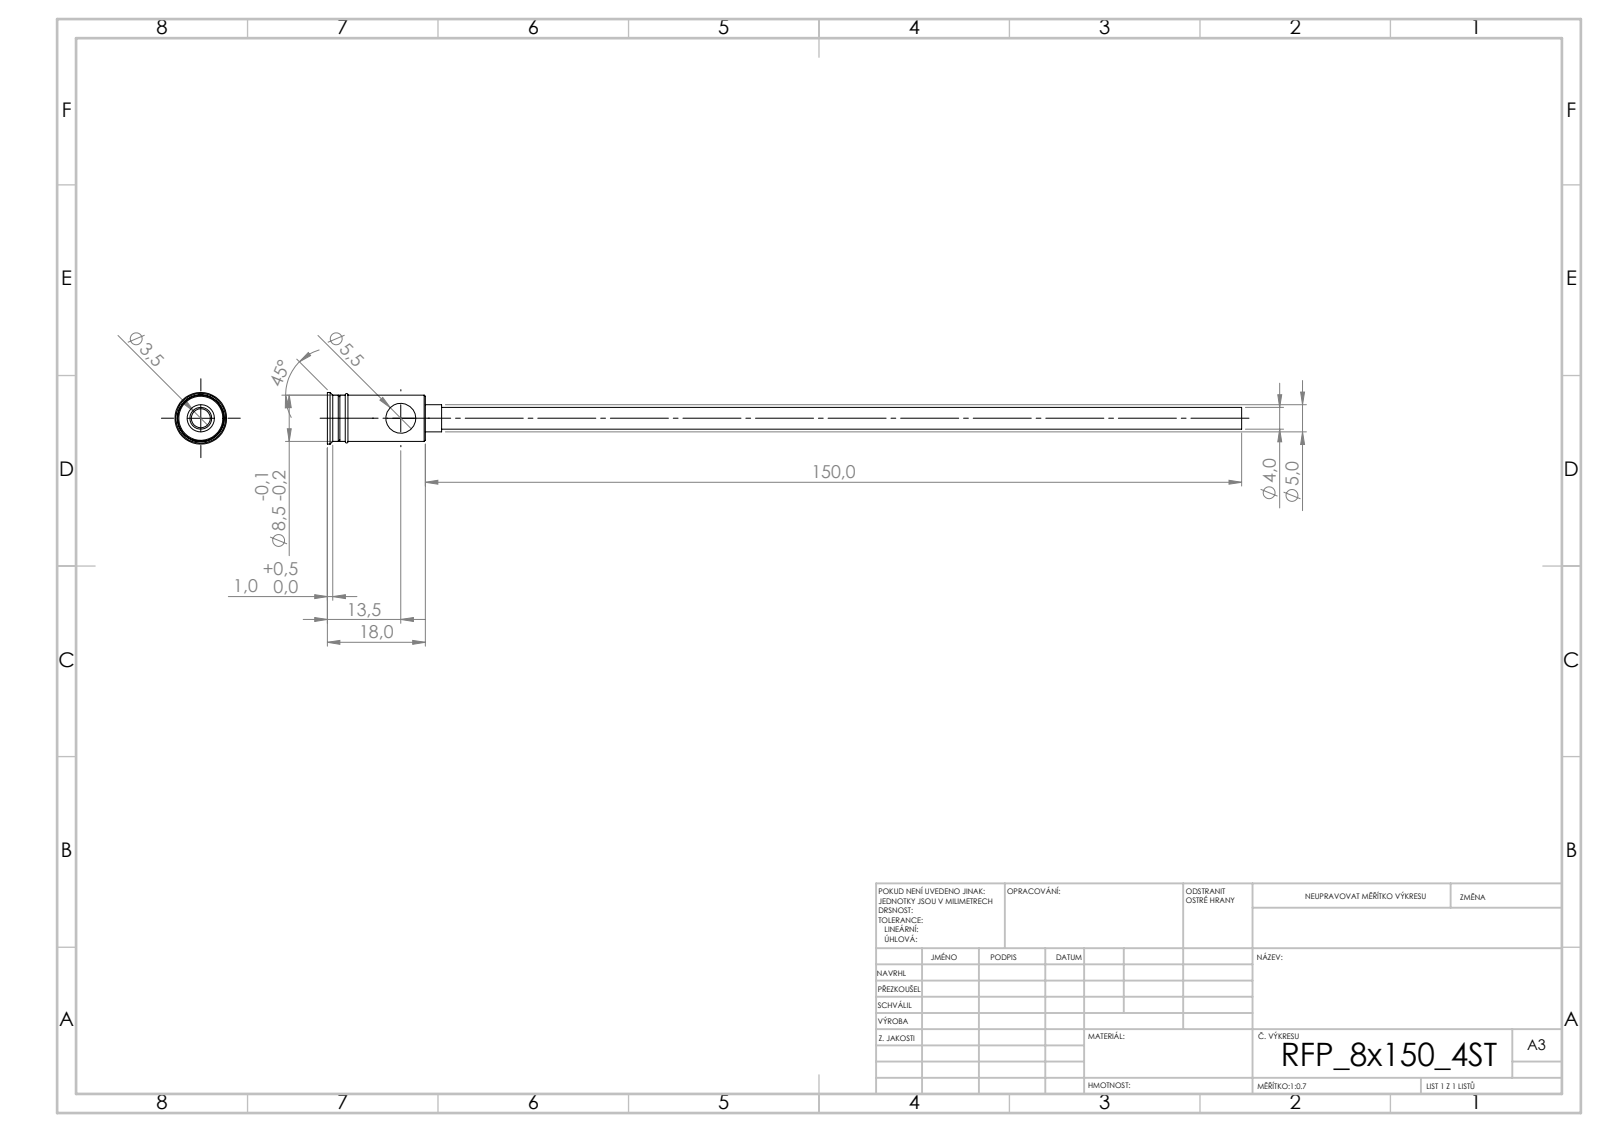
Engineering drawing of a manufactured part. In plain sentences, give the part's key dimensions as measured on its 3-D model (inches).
Its 3-D file was written by "SolidWorks 2019 (CONFIG_CONTROL_DESIGN)". It is 1 solid with 44 faces: 20 planar, 16 cylindrical and 8 other. Overall it measures 6.614 by 0.374 by 0.374 inches. Its volume is 0.077 cubic inches and its surface area 6.645 square inches. Round holes: 1 of diameter 0.138, 1 of diameter 0.217. Round bosses or shafts: 1 of diameter 0.374, 1 of diameter 0.335, 1 of diameter 0.197, 1 of diameter 0.157. The main face-to-face distances are 0.709, 0.63, 0.079, 0.154, 0.618, 0.091, 0.118, 0.736, 0.748, 0.827.
